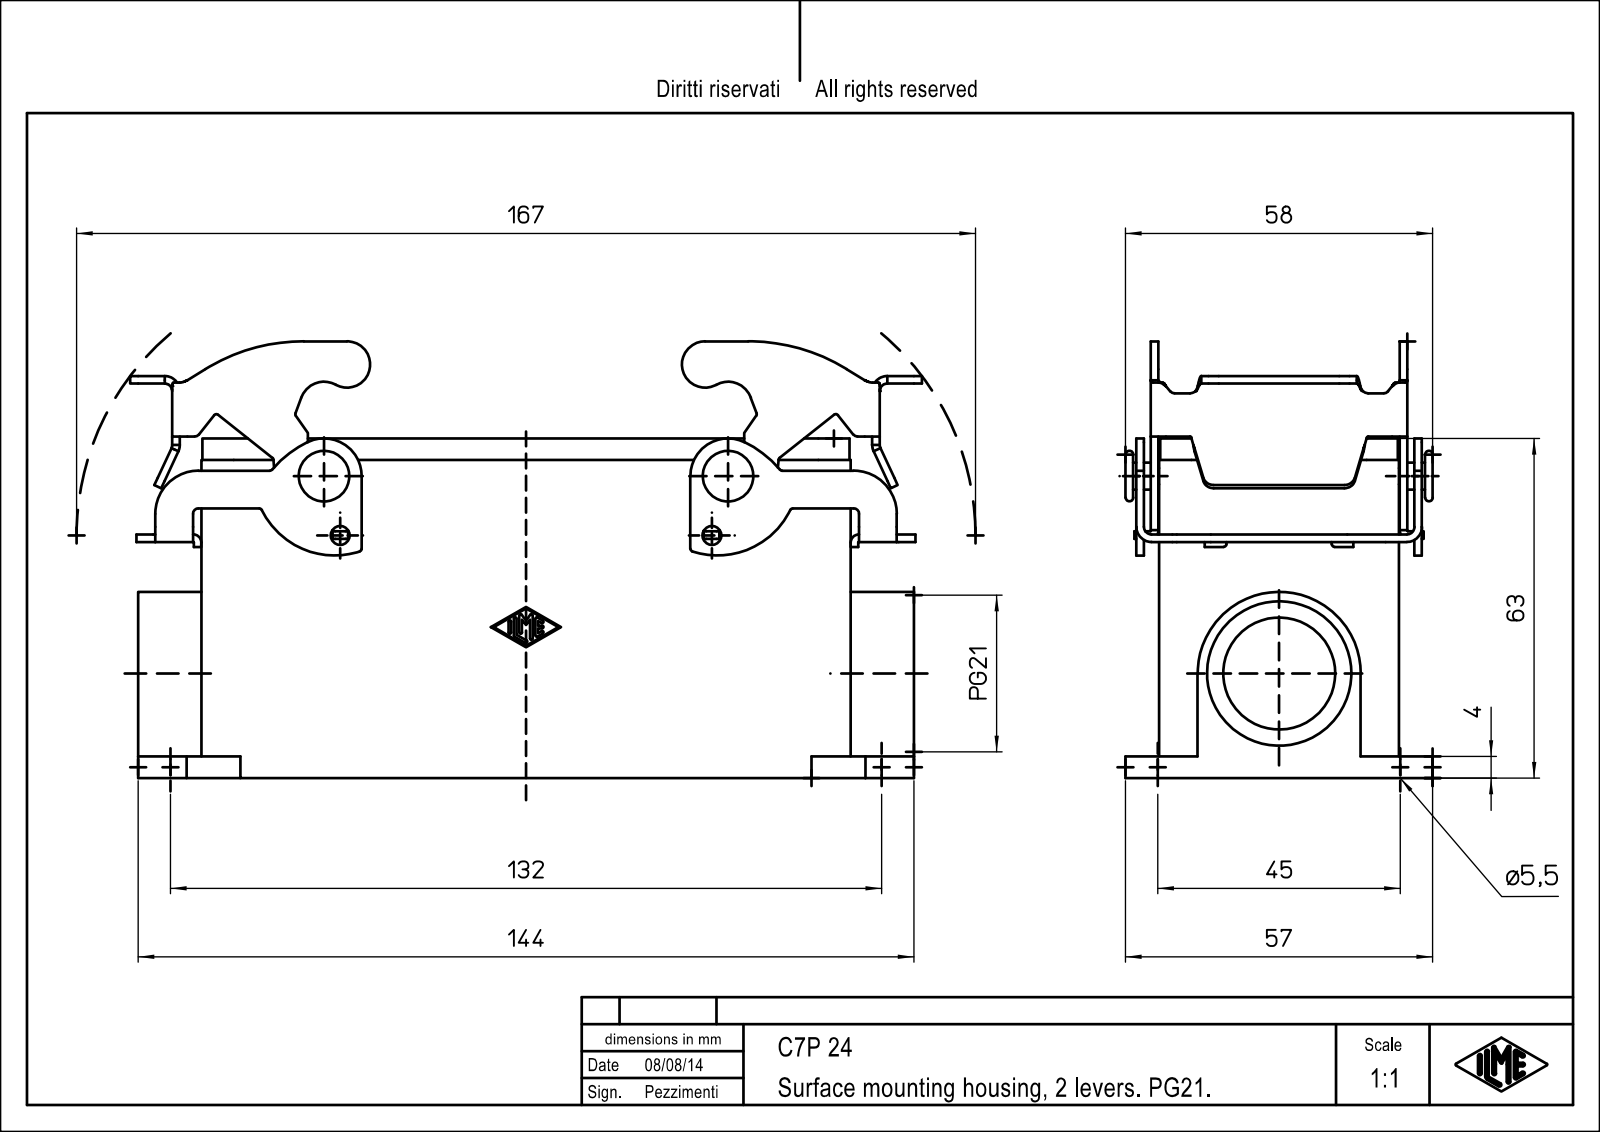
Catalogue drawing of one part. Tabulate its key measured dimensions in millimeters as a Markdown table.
| quantity | value |
| --- | --- |
| part name | p1; p2; p3; JCVP_24 (+1 more) |
| STEP written by | Creo Elements/Direct Modeling 18.0B 02-Dec-2011 (C) Parametric Technology GmbH (AUTOMOTIVE_DESIGN) |
| units | millimeters |
| bodies | 3 solids, 609 faces (293 planar, 272 cylindrical, 44 other) |
| overall size | 146.97 × 81 × 57 |
| volume | 129 618 mm³ |
| surface area | 71 734 mm² |
| round holes (diameter × count) | 2.46 × 4, 3 × 4, 5.5 × 4, 3.5 × 2, 20.78 × 1, 26.78 × 1 |
| round bosses / shafts (diameter × count) | 5 × 2, 3.2 × 2, 3 × 2 |
| partial cylindrical surfaces (radius × count) | 0.5 × 22, 1 × 18, 0.25 × 16, 1.5 × 14, 2 × 12, 1.4 × 10, 2.8 × 10, 8 × 6 |
| main face-to-face distances | 4, 40.5, 1.4, 44.5, 36.5, 2.7, 48.9, 11.75, 8.25, 4.15 |
| hole center spacings | 16.64, 38.63, 118.34, 123.37, 27, 45, 104, 107.45 |
